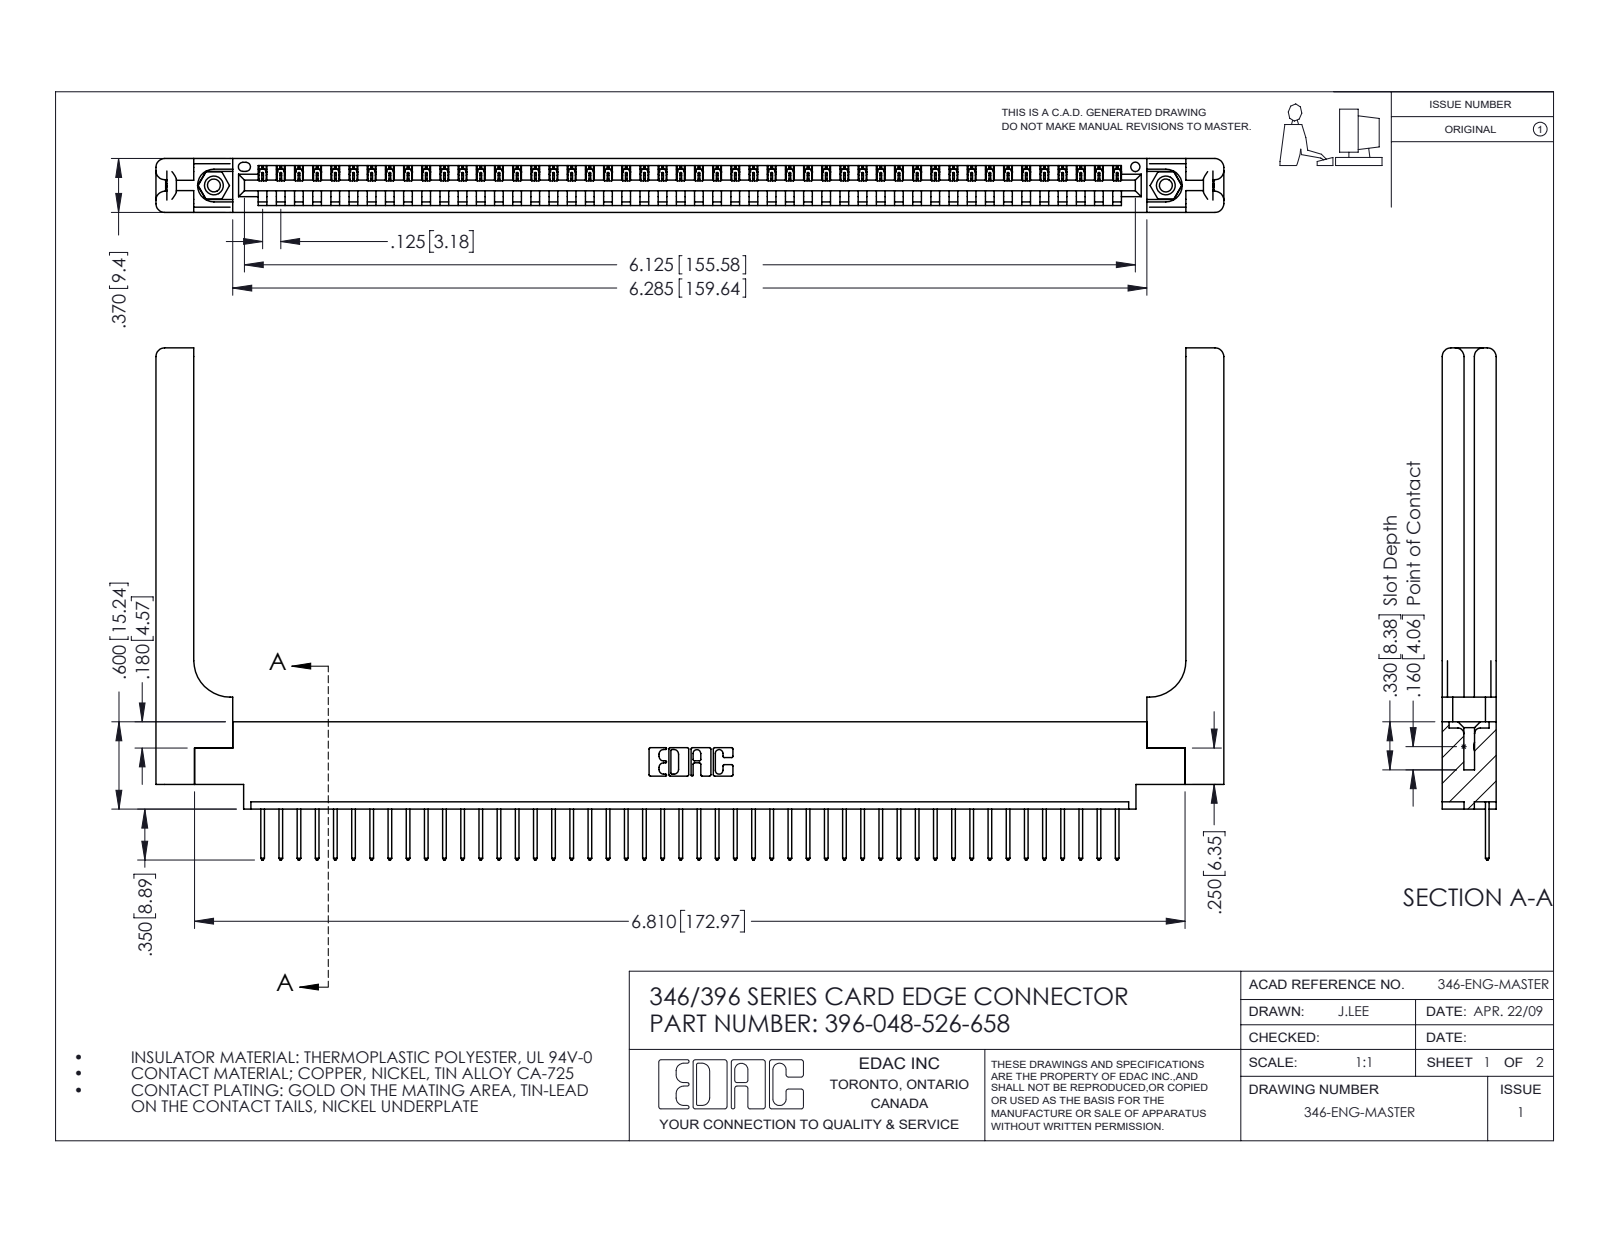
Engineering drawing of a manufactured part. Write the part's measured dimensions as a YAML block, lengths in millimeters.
part_name: "396-048-526-658; 346-220-058_345-220-058; 345-250-001_345-250-001-102; 345-292-001_345-293-126 (+1 more)"
step_written_by: "SolidWorks 2016 (CONFIG_CONTROL_DESIGN)"
units: millimeters
bodies: {solids: 53, faces: 3166, planar: 2148, cylindrical: 958, other: 60}
overall_size: [186.5, 89.4, 9.4]
volume: 25220
surface_area: 27460
round_holes:
  - {diameter: 2.3, count: 2}
  - {diameter: 3.2, count: 2}
  - {diameter: 4, count: 2}
  - {diameter: 1.6, count: 1}
round_bosses_or_shafts:
  - {diameter: 3.9, count: 2}
partial_cylinders:
  - {radius: 0.2, count: 96}
  - {radius: 0.3, count: 96}
  - {radius: 0.3, count: 22}
  - {radius: 1.5, count: 16}
  - {radius: 0.2, count: 6}
  - {radius: 0.8, count: 6}
  - {radius: 0.7, count: 3}
  - {radius: 0.8, count: 2}
face_to_face_distances: [9.4, 1.2, 8.2, 1.8, 3.8, 3.8, 6.4, 7.6, 0.6, 5.6]
hole_center_spacings: [6.2, 160.9, 166.2]
